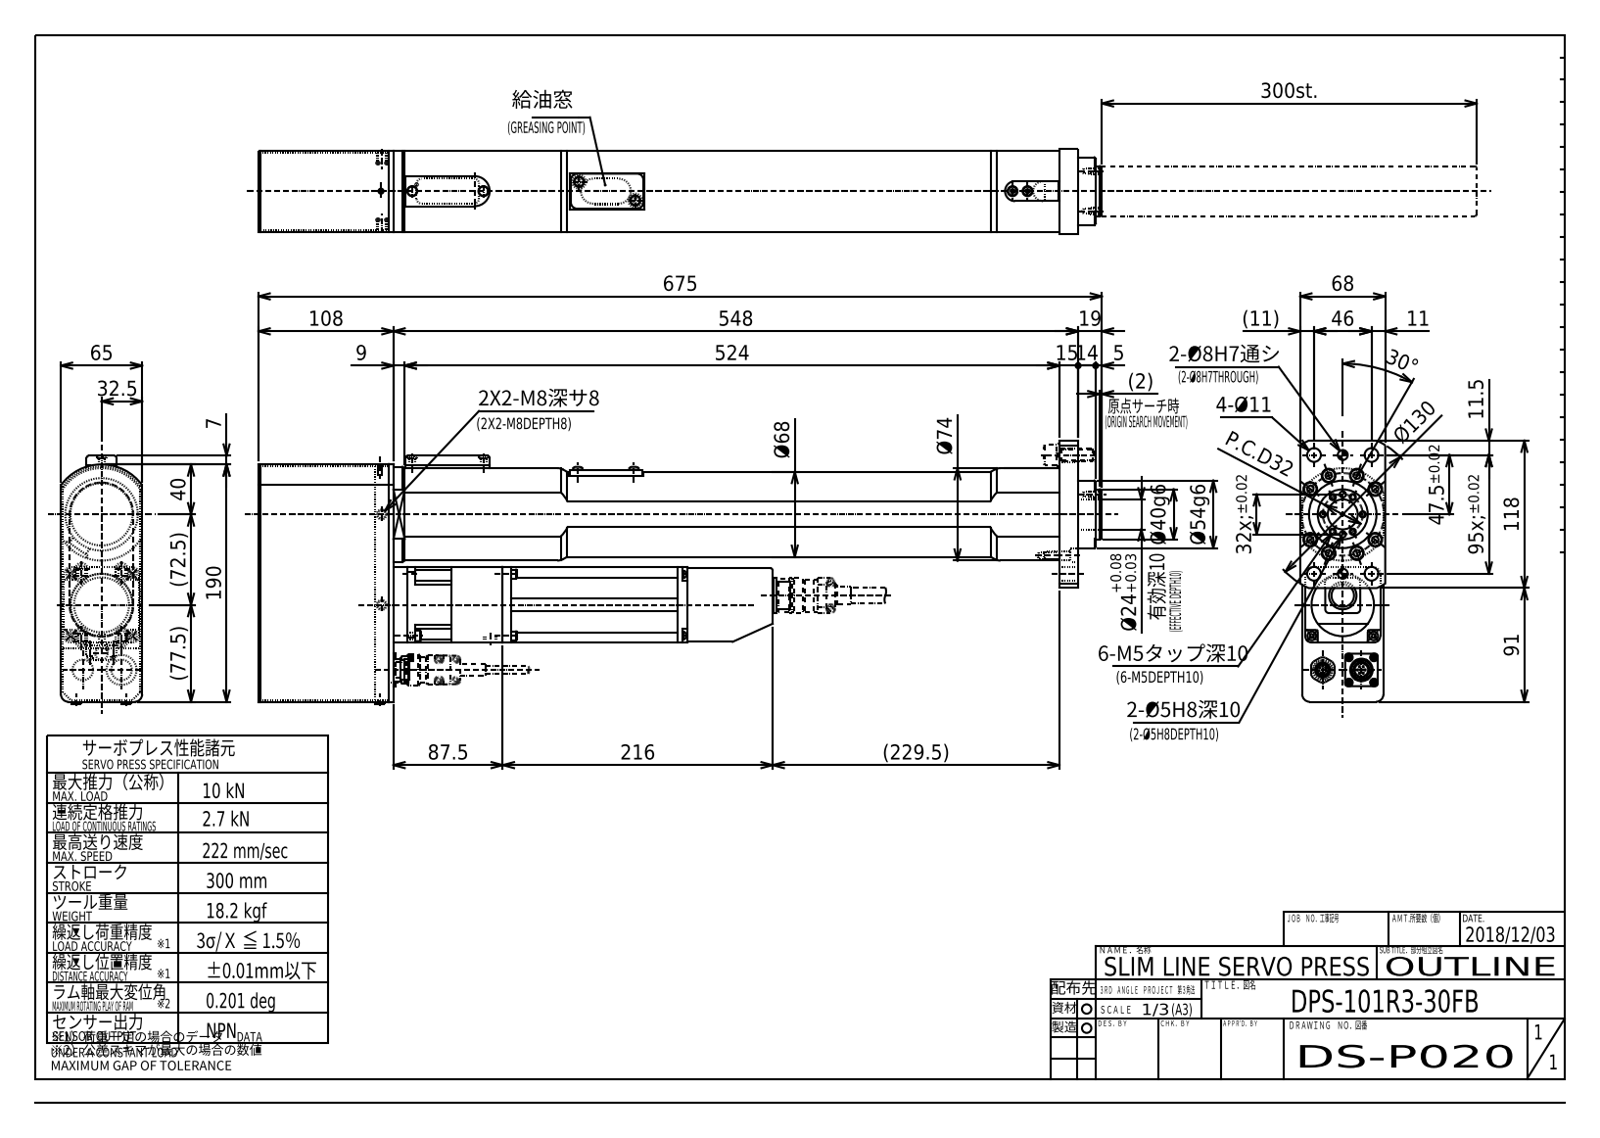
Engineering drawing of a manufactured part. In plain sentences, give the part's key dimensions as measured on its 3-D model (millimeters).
The part is named "DPS-101R3-30FB(DS-P020)_OUTLINE; DPS-051R3-30FB_OUTLINE; DS-P020-02_OUTLINE". Its 3-D file was written by "Autodesk Inventor 2017 (AUTOMOTIVE_DESIGN)". It is 3 solids with 768 faces: 363 planar, 234 cylindrical and 171 other. Overall it measures 675 by 209 by 68 millimeters. Its volume is 4 263 000 cubic millimeters and its surface area 426 431 square millimeters. Round holes: 10 of diameter 4.5, 7 of diameter 3.24, 6 of diameter 4.13, 6 of diameter 8, 5 of diameter 11, 4 of diameter 3.3, 4 of diameter 5, 4 of diameter 5.5, 2 of diameter 2.46, 2 of diameter 8.5, 1 of diameter 4, 1 of diameter 8.7. Round bosses or shafts: 1 of diameter 68, 1 of diameter 59, 1 of diameter 54, 1 of diameter 25.5, 1 of diameter 23.5, 1 of diameter 22, 1 of diameter 21.91, 1 of diameter 20.7. Partial cylindrical surfaces (rounded edges, fillets, slot ends): 31 of radius 2, 16 of radius 5, 8 of radius 0.5, 4 of radius 2.5, 3 of radius 10, 2 of radius 3, 2 of radius 4.5, 2 of radius 6. The main face-to-face distances are 65, 2.5, 60, 62.5, 15, 11, 107.5, 47.5, 49, 656. The hole center spacings are 16, 8.28, 22.63, 23, 27.71, 30.91, 34.58, 36.83.
